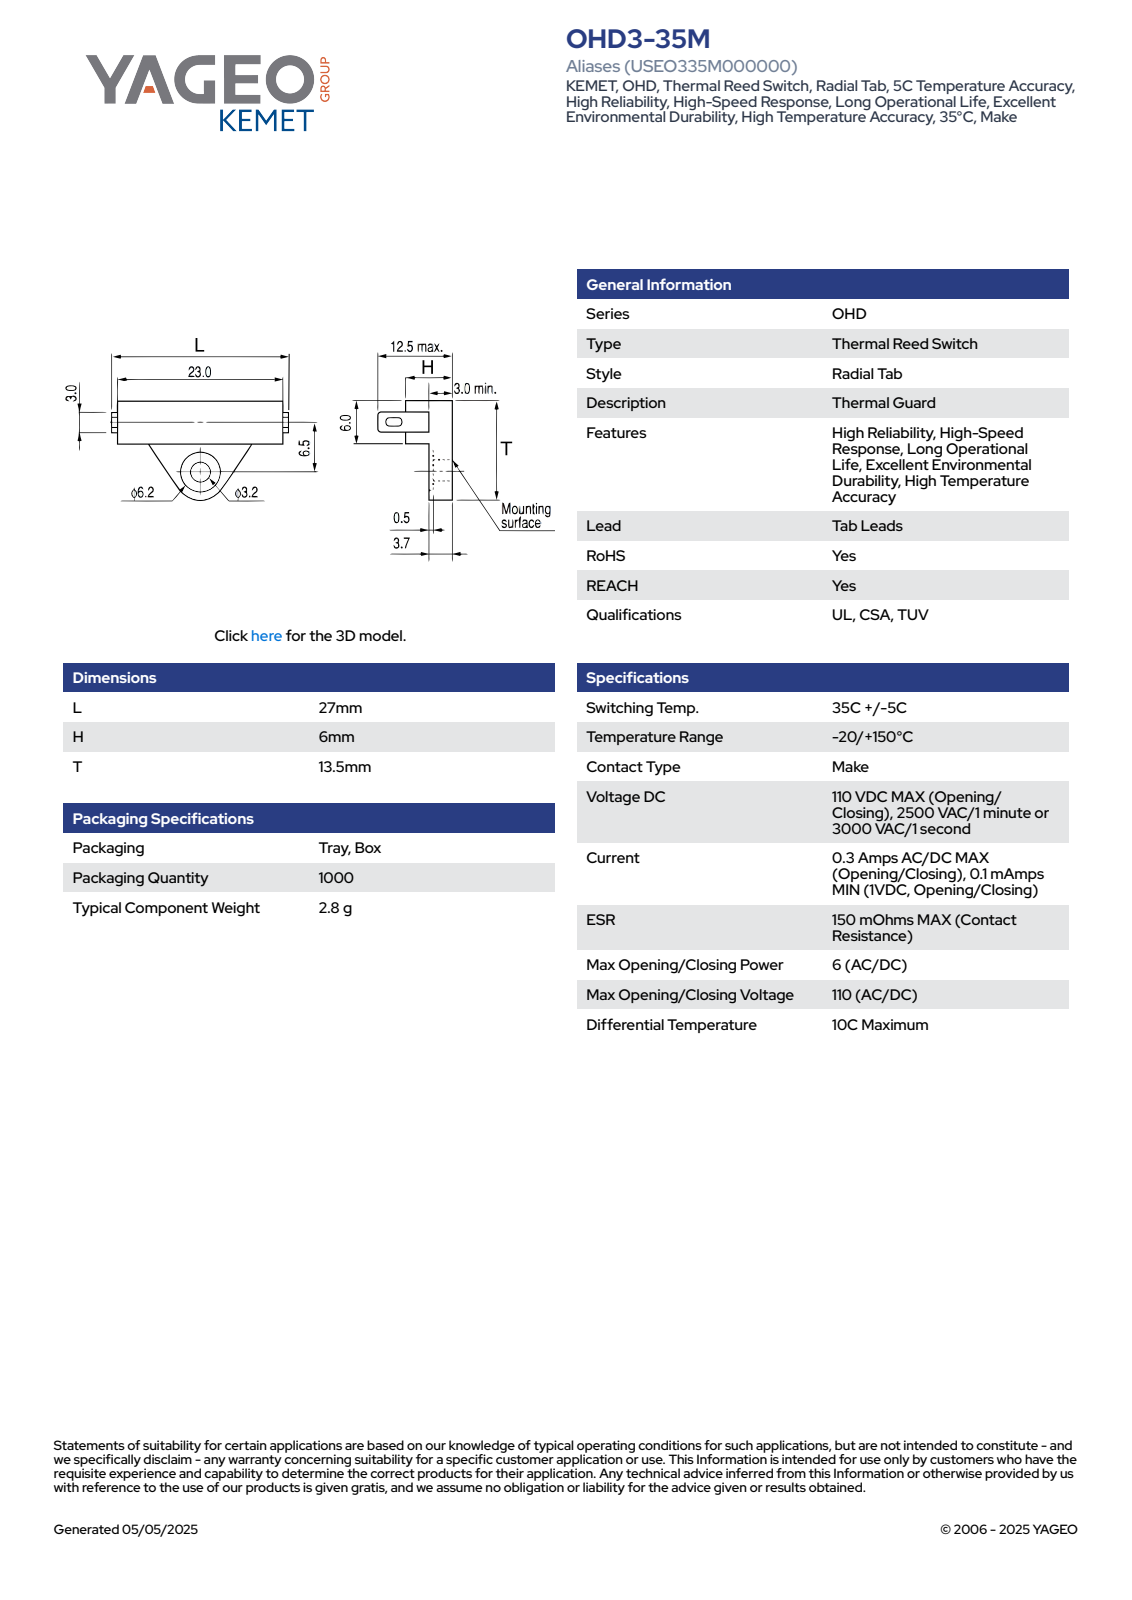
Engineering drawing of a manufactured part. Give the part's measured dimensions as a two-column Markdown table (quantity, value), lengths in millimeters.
| quantity | value |
| --- | --- |
| part name | Default |
| STEP written by | SolidWorks 2014 (AUTOMOTIVE_DESIGN) |
| units | millimeters |
| bodies | 2 solids, 111 faces (89 planar, 22 cylindrical, 0 other) |
| overall size | 27 × 13.5 × 12.5 |
| volume | 1 092 mm³ |
| surface area | 1 078 mm² |
| round holes (diameter × count) | 3.2 × 1, 6.2 × 1 |
| partial cylindrical surfaces (radius × count) | 0.4 × 8, 0.2 × 4, 0.5 × 2, 4 × 2 |
| main face-to-face distances | 6, 0.65, 3.7, 2.3, 23, 1.5, 4.5, 3, 0.5, 3.2 |
